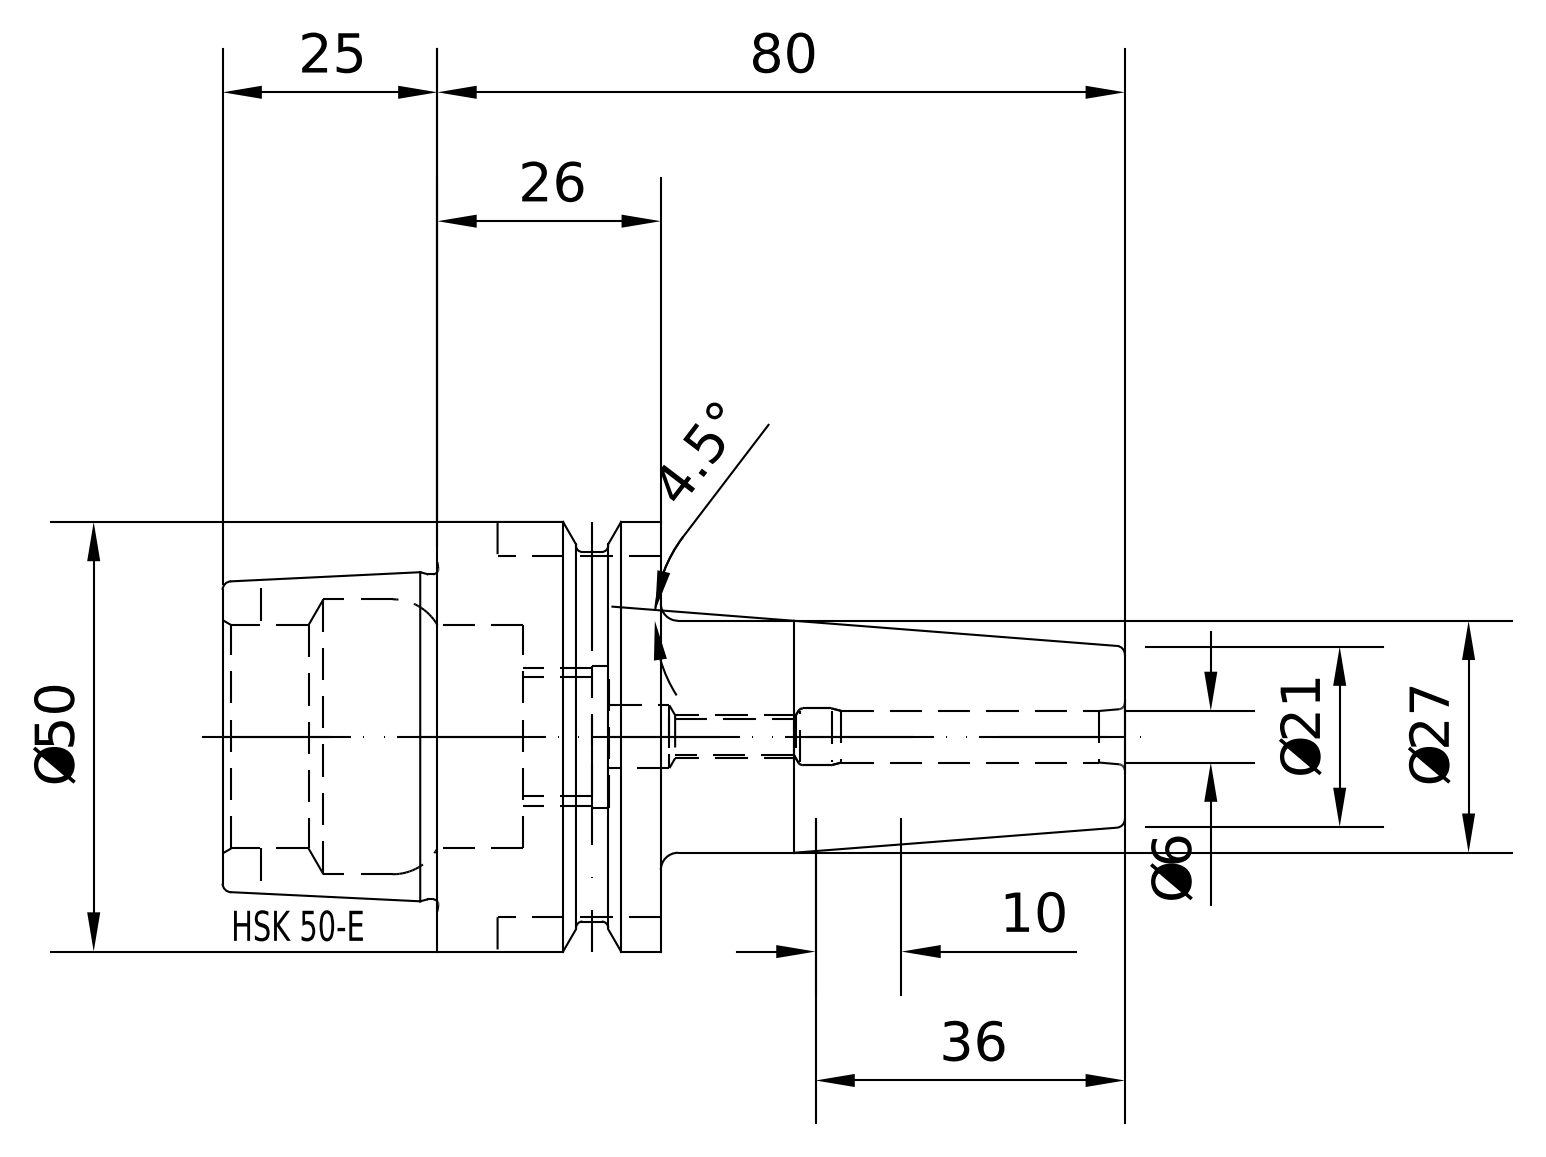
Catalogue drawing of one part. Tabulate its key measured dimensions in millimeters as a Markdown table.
| quantity | value |
| --- | --- |
| part name | E50-140-06 |
| STEP written by | PRO/ENGINEER BY PARAMETRIC TECHNOLOGY CORPORATION, 2010430 (CONFIG_CONTROL_DESIGN) |
| units | millimeters |
| bodies | 1 solid, 79 faces (9 planar, 24 cylindrical, 46 other) |
| overall size | 104.9 × 50 × 50 |
| volume | 77 106 mm³ |
| surface area | 19 674 mm² |
| round holes (diameter × count) | 6 × 1, 14 × 1, 16.32 × 1, 16.5 × 1, 26.04 × 1, 32.08 × 1 |
| round bosses / shafts (diameter × count) | 50 × 1, 42.95 × 1, 37.91 × 1, 27 × 1 |
| main face-to-face distances | 25.95, 24.9, 50.85, 104.9, 80, 54.05, 34.85, 9.95, 16, 70.05 |
